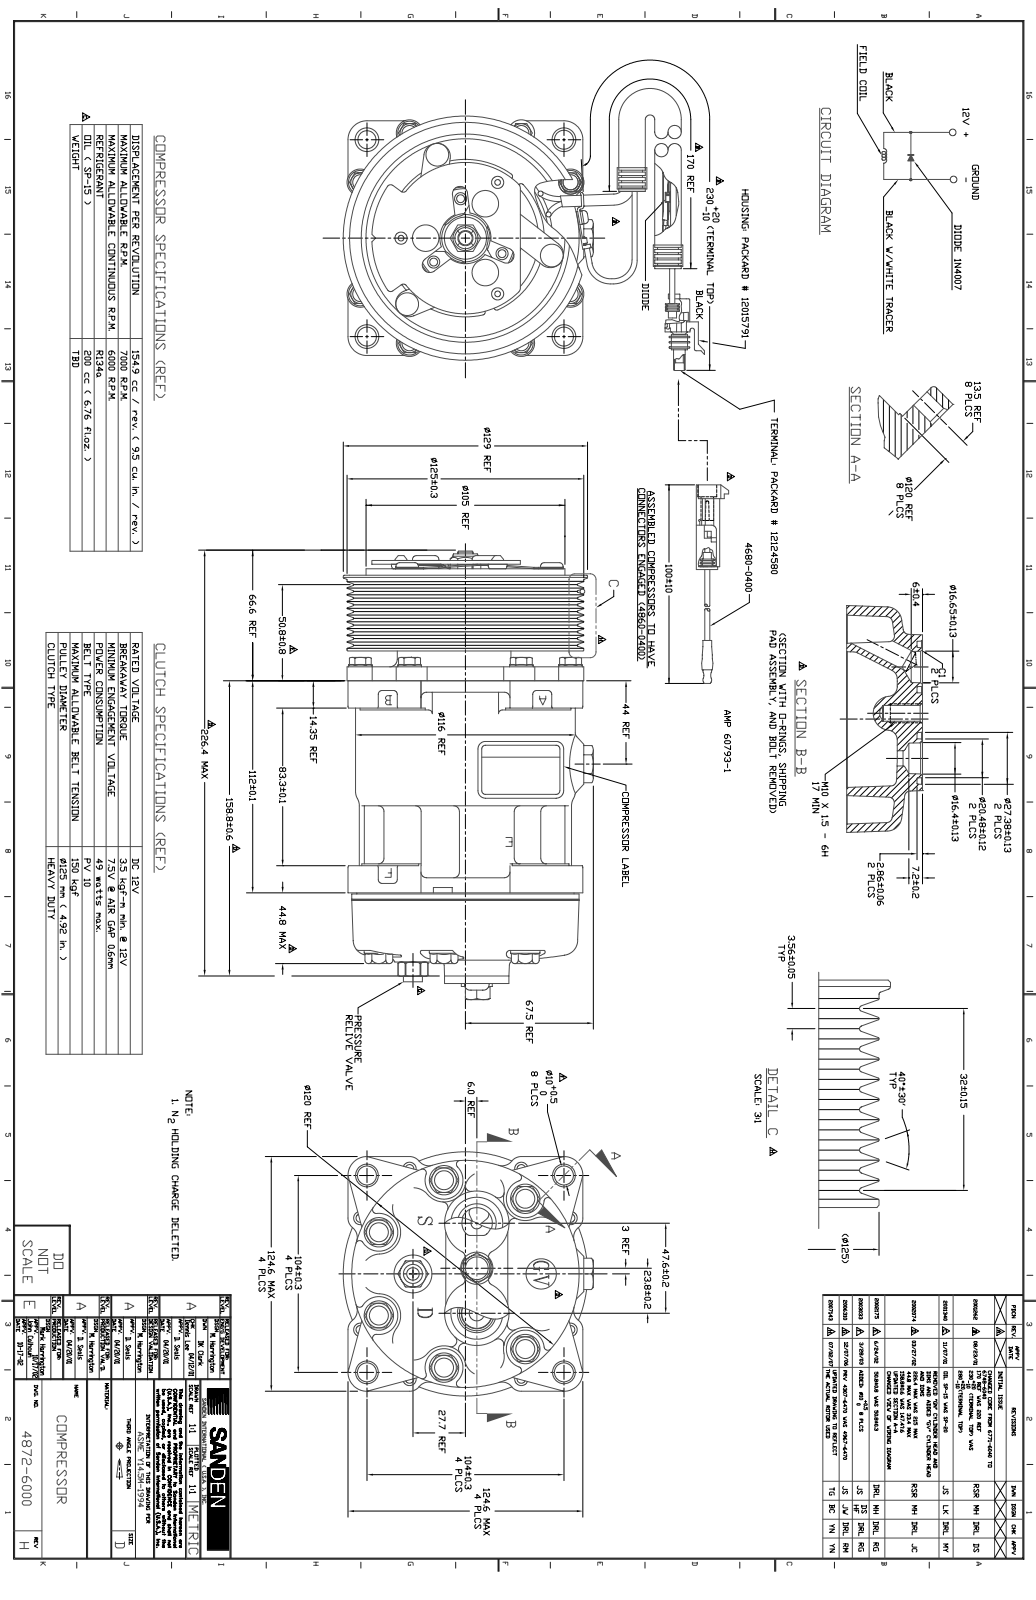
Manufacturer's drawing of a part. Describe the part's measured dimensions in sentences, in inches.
The part is named "4872". Its 3-D file was written by "SolidWorks 2007 (CONFIG_CONTROL_DESIGN)". It is 1 solid with 2658 faces: 707 planar, 679 cylindrical and 1272 other. Overall it measures 17.336 by 9.072 by 5.079 inches. Its volume is 137.3 cubic inches and its surface area 406.6 square inches. Round holes: 9 of diameter 0.335, 8 of diameter 0.217, 6 of diameter 0.469, 4 of diameter 0.315, 4 of diameter 0.404, 3 of diameter 0.2, 3 of diameter 0.26, 2 of diameter 0.087, 2 of diameter 1.078, 1 of diameter 0.043, 1 of diameter 0.138, 1 of diameter 0.197. Round bosses or shafts: 8 of diameter 0.508, 6 of diameter 0.602, 6 of diameter 0.106, 3 of diameter 0.551, 3 of diameter 0.472, 3 of diameter 0.394, 3 of diameter 0.311, 3 of diameter 0.256. Partial cylindrical surfaces (rounded edges, fillets, slot ends): 33 of radius 0.276, 31 of radius 0.079, 26 of radius 0.039, 25 of radius 0.256, 24 of radius 0.118, 19 of radius 0.197, 13 of radius 0.157, 12 of radius 0.059. The main face-to-face distances are 0.079, 1.832, 1.769, 0.173, 0.339, 1.99, 0.22, 0.331, 0.321, 1.448. The hole center spacings are 0.896, 2.474, 3.212, 4.324, 5.311, 1.999, 2.895, 3.5.
